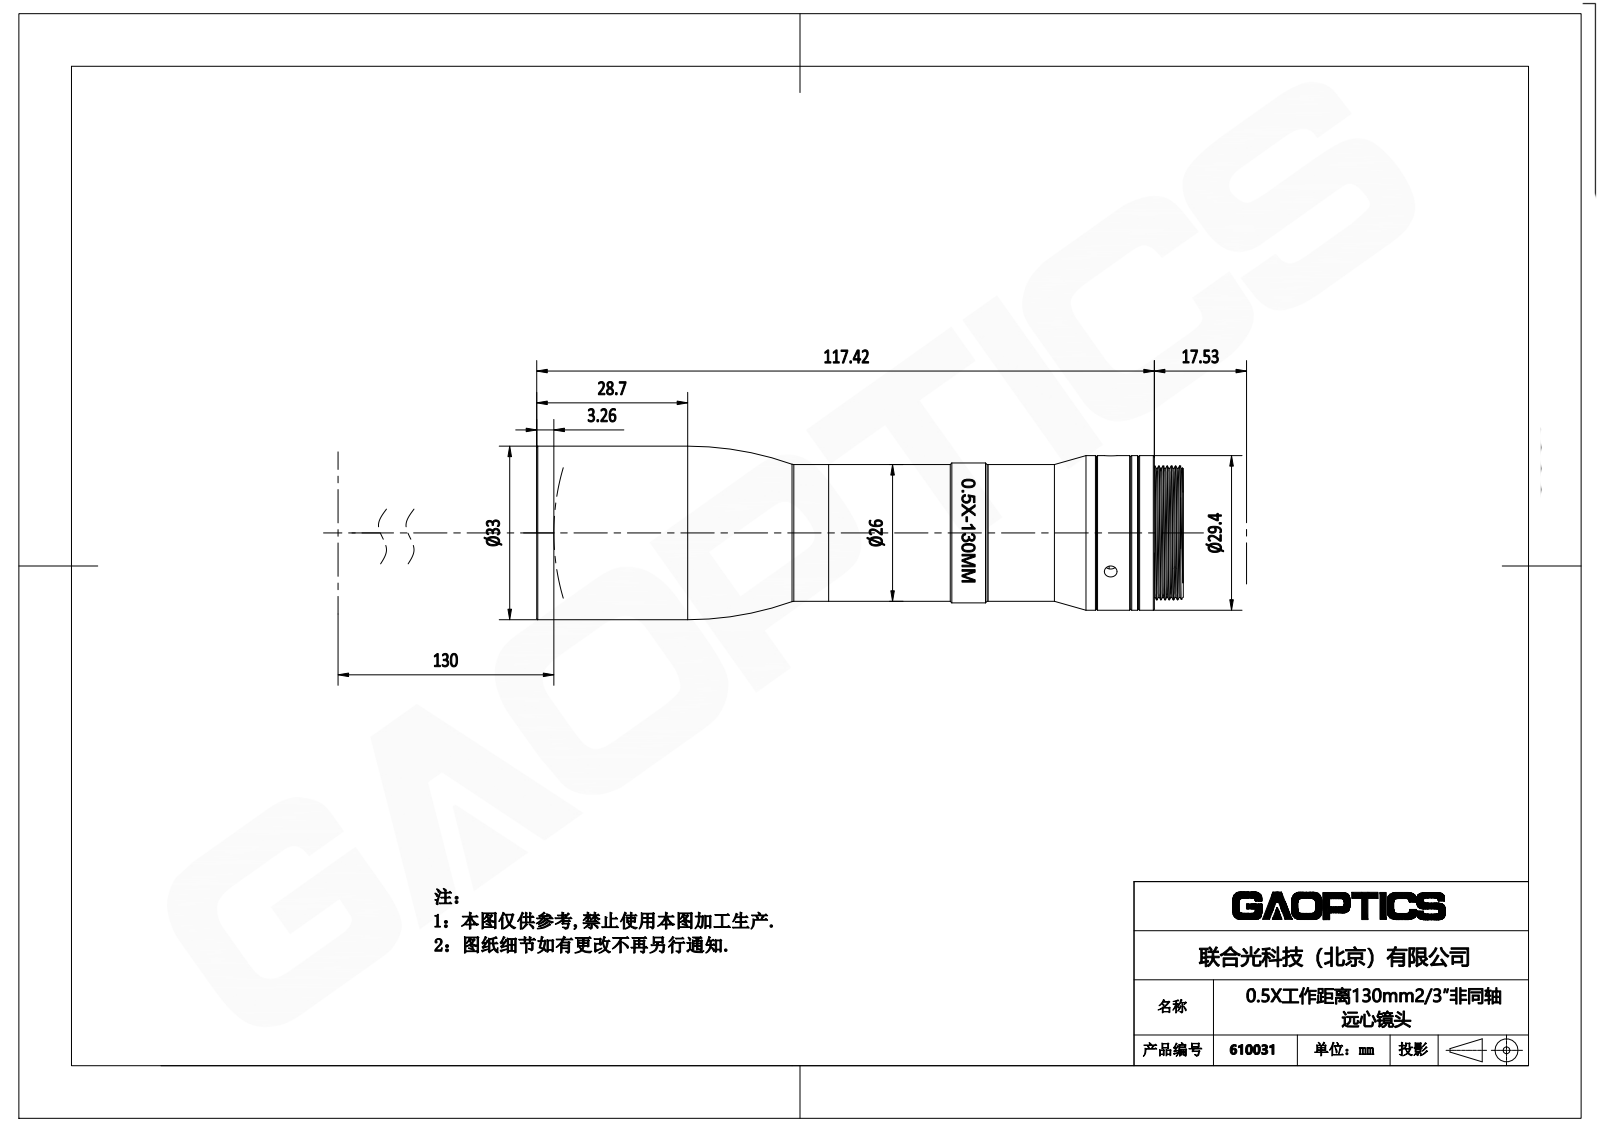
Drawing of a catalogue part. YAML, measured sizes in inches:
part_name: "610031"
step_written_by: "SolidWorks 2020 (CONFIG_CONTROL_DESIGN)"
units: inches
bodies: {solids: 15, faces: 466, planar: 145, cylindrical: 242, other: 79}
overall_size: [4.812, 1.299, 1.299]
volume: 5.782
surface_area: 71.51
round_holes:
  - {diameter: 0.094, count: 3}
  - {diameter: 0.043, count: 1}
  - {diameter: 0.117, count: 1}
  - {diameter: 0.118, count: 1}
  - {diameter: 0.244, count: 1}
  - {diameter: 0.295, count: 1}
  - {diameter: 0.315, count: 1}
  - {diameter: 0.335, count: 1}
  - {diameter: 0.354, count: 1}
  - {diameter: 0.374, count: 1}
  - {diameter: 0.394, count: 1}
  - {diameter: 0.413, count: 1}
round_bosses_or_shafts:
  - {diameter: 1.299, count: 1}
  - {diameter: 1.201, count: 1}
  - {diameter: 1.157, count: 1}
  - {diameter: 1.024, count: 1}
  - {diameter: 1, count: 1}
  - {diameter: 0.995, count: 1}
  - {diameter: 0.957, count: 1}
  - {diameter: 0.921, count: 1}
partial_cylinders:
  - {radius: 0.02, count: 2}
  - {radius: 0.03, count: 1}
face_to_face_distances: [0.059, 0.118, 3.701, 3.588, 0.113, 2.73, 0.858, 0.971, 3.844, 1.114]
